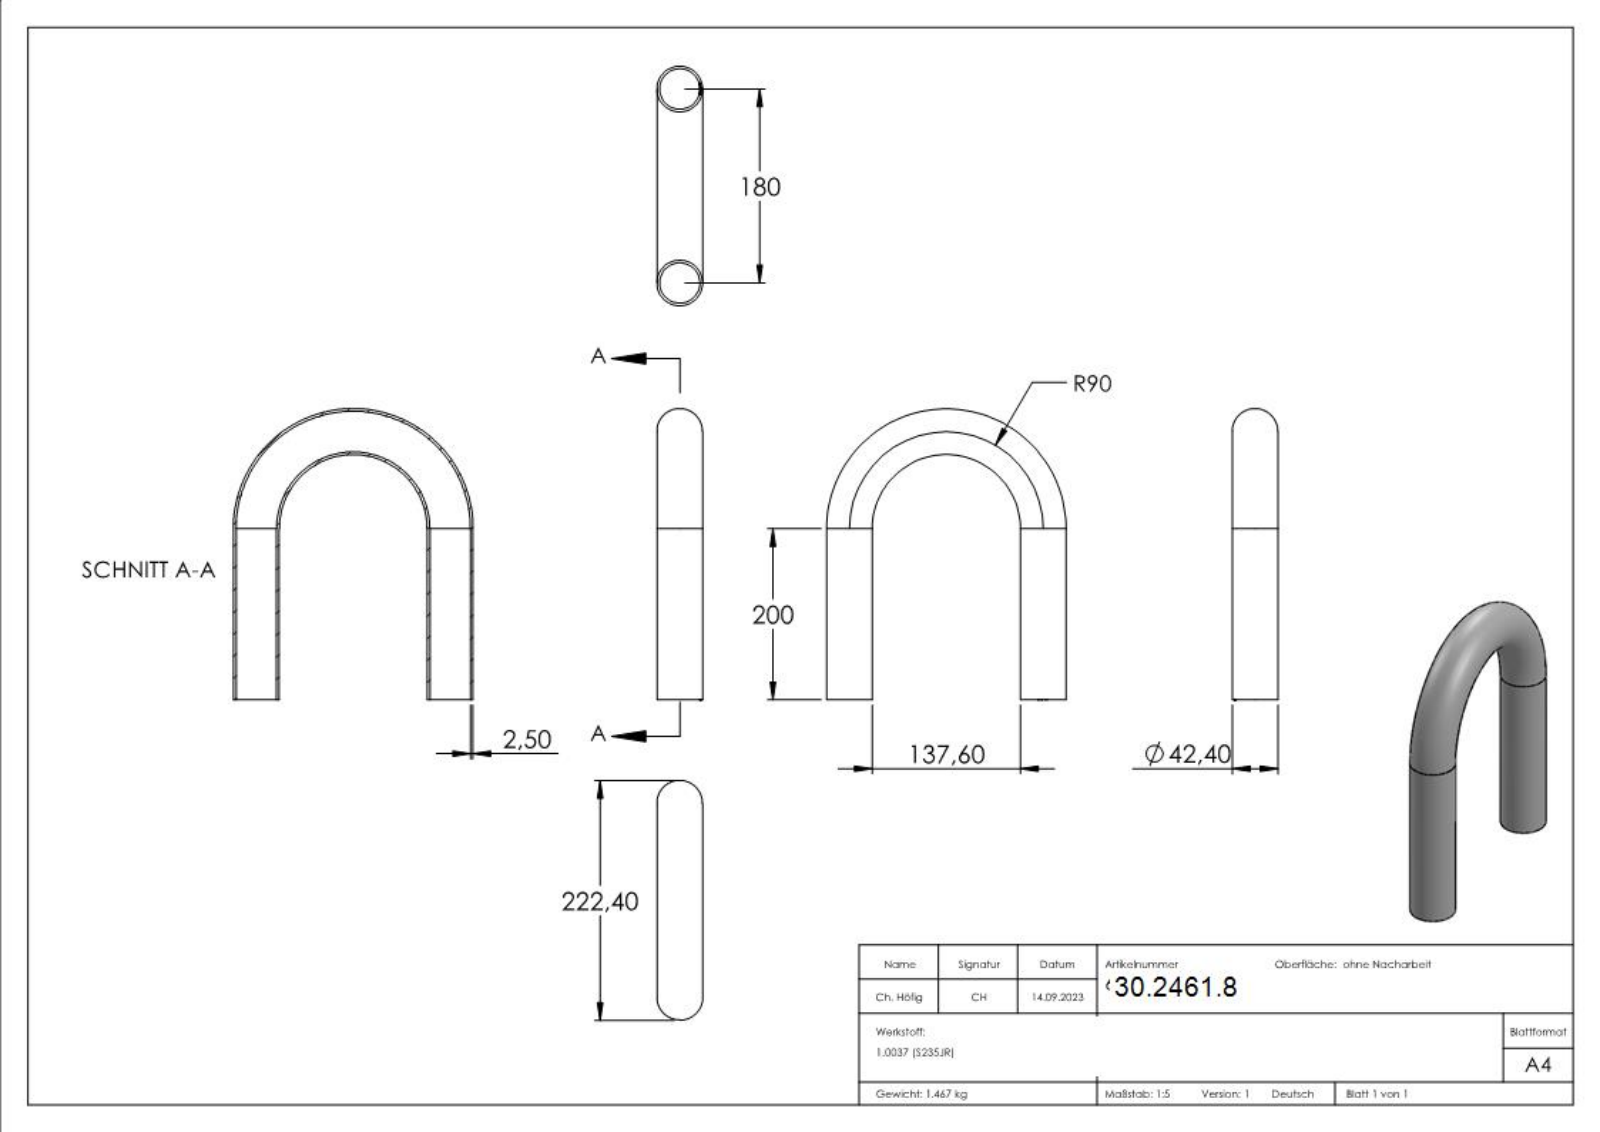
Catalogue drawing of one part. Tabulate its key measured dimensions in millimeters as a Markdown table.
| quantity | value |
| --- | --- |
| part name | 6967-U090 |
| STEP written by | SolidWorks 2018 (CONFIG_CONTROL_DESIGN) |
| units | millimeters |
| bodies | 1 solid, 225 faces (110 planar, 4 cylindrical, 111 other) |
| overall size | 269.83 × 222.4 × 42.4 |
| volume | 188 024 mm³ |
| surface area | 151 052 mm² |
| round holes (diameter × count) | 37.4 × 2 |
| round bosses / shafts (diameter × count) | 42.4 × 2 |
| main face-to-face distances | 0.44, 0.4, 0.36, 0.32, 0.47, 0.51, 0.39, 0.52, 0.79, 1.75 |
| hole center spacings | 180 |
